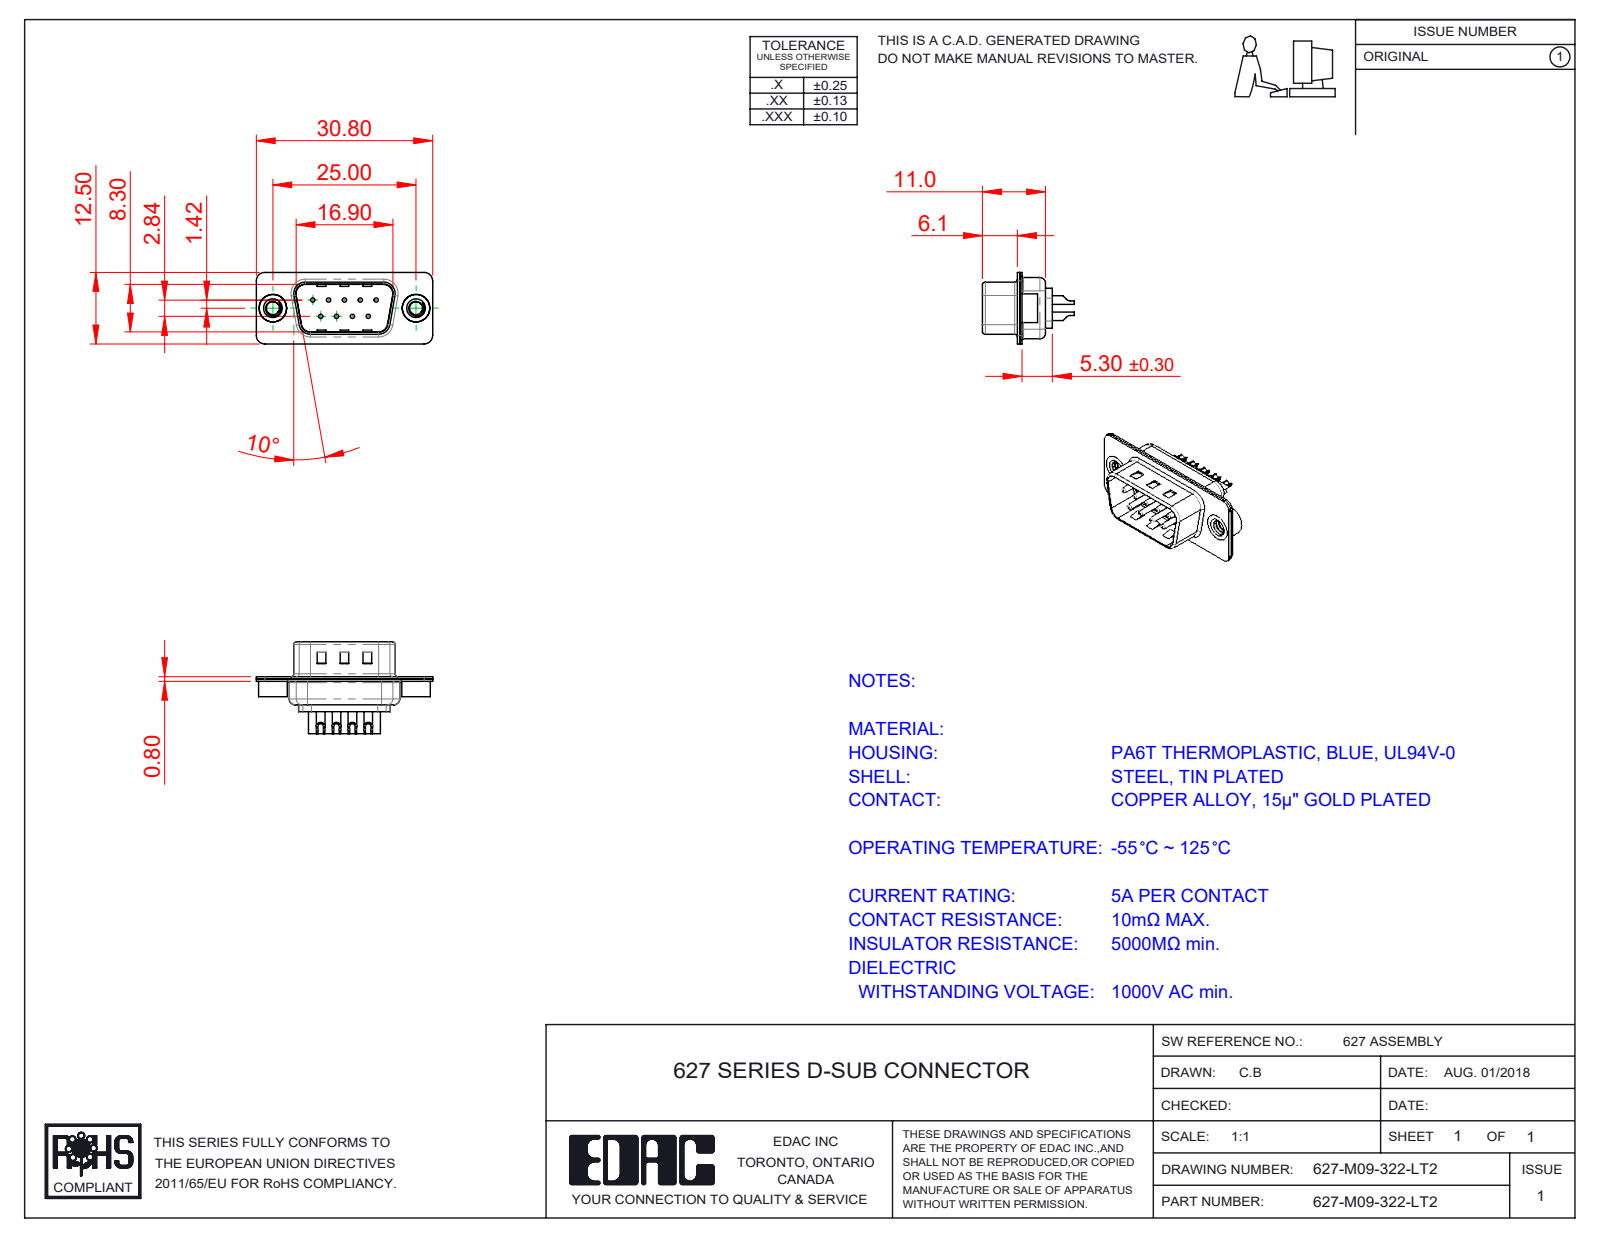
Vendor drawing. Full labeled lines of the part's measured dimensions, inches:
Part name (STEP PRODUCT): 627M Contact Row 2_22; 627M Shell Front_09 Contacts; 627-M09-322-LT2; 627M Shell Rear_09 Contacts (+3 more)
STEP written by: SolidWorks 2020 (CONFIG_CONTROL_DESIGN)
Units: inches
Bodies: 14 solids, 637 faces (188 planar, 273 cylindrical, 176 other)
Overall size (bounding box): 1.213 × 0.632 × 0.492
Volume: 0.081 in³ · Surface area: 5.67 in²
Round holes (diameter × count): ⌀0.03 ×9, ⌀0.039 ×9, ⌀0.063 ×9, ⌀0.079 ×9, ⌀0.089 ×2, ⌀0.157 ×2, ⌀0.189 ×2
Round bosses / shafts (diameter × count): ⌀0.059 ×9, ⌀0.197 ×2, ⌀0.193 ×2
Partial cylindrical surfaces — rounded edges, fillets, slot ends (radius × count): R0.059 ×16, R0.079 ×12, R0.02 ×8, R0.063 ×8, R0.039 ×6, R0.01 ×4, R0.024 ×4, R0.026 ×4
Main face-to-face distances: 0.016, 0.031, 0.374, 0.358, 0.343, 0.026, 0.39, 0.047, 0.03, 0.014
Hole centre spacings: 0.124, 0.109, 0.218, 0.198, 0.198, 0.327, 0.28, 0.294
